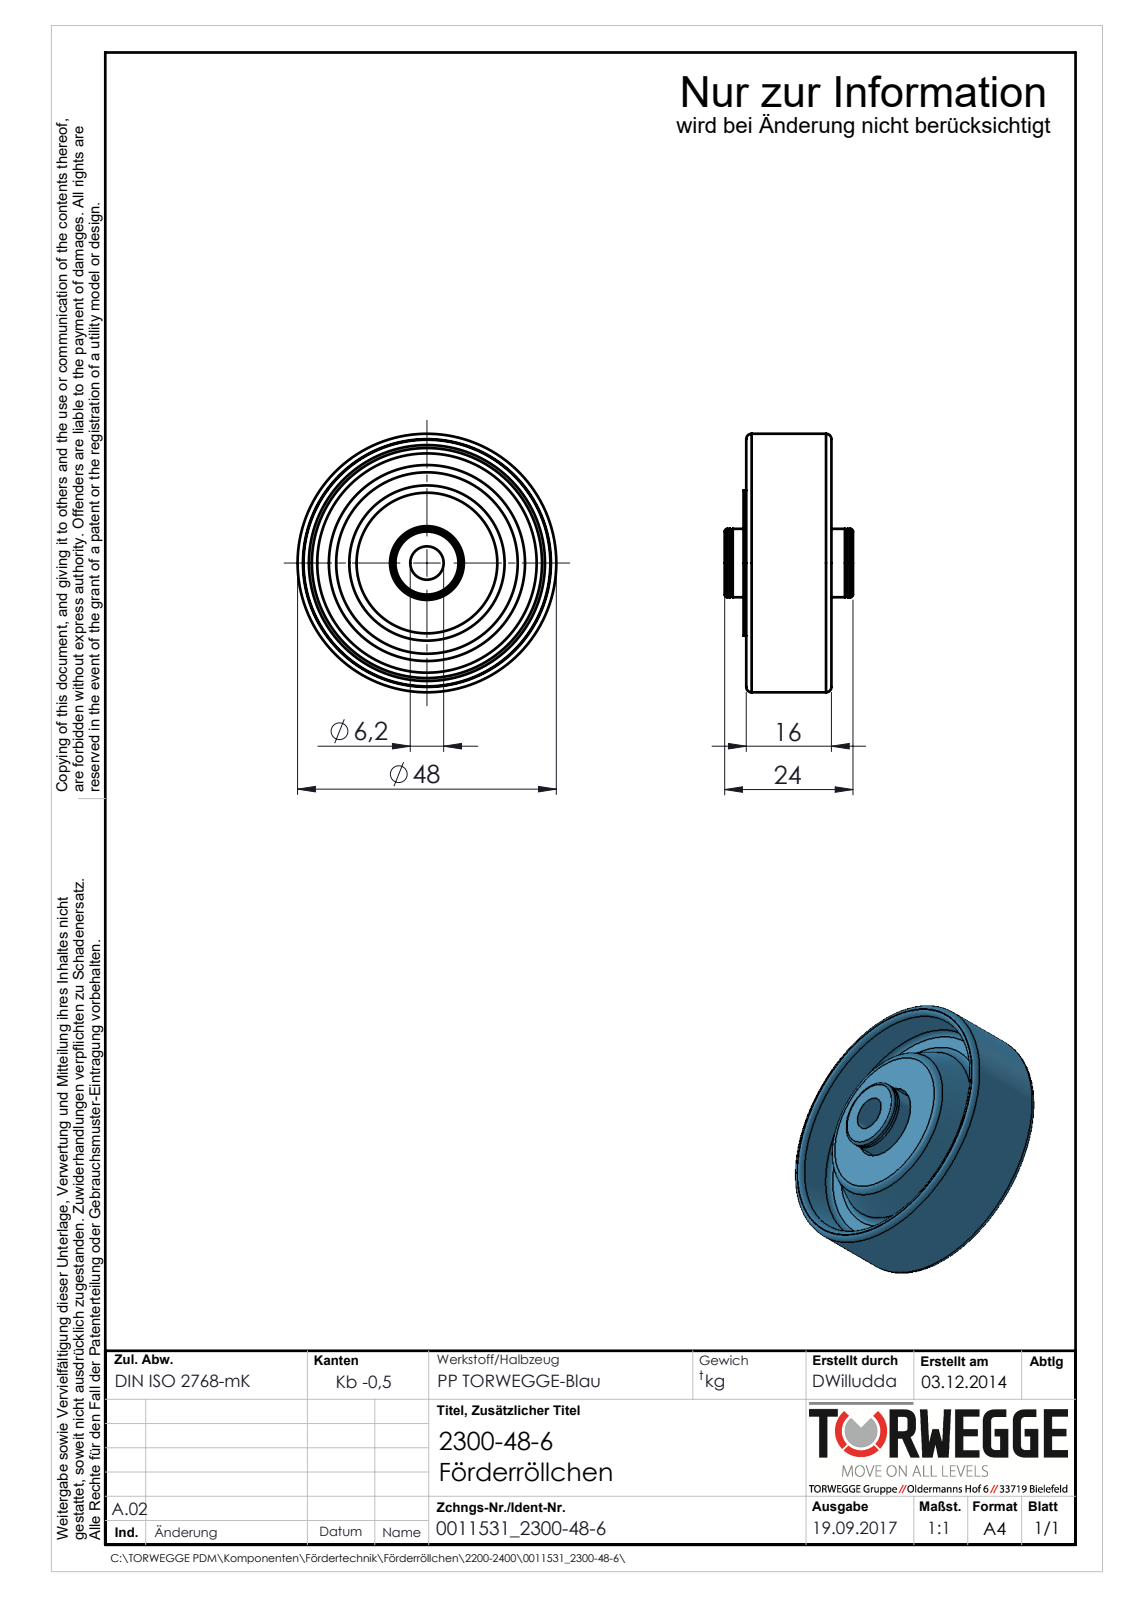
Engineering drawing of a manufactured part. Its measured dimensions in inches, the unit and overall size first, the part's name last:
Units: inches
Overall size (bounding box): 1.89 × 1.89 × 0.937
Round holes (diameter × count): ⌀0.244 ×1, ⌀0.539 ×1
Round bosses / shafts (diameter × count): ⌀1.89 ×1, ⌀1.063 ×1, ⌀0.5 ×1
Main face-to-face distances: 0.642, 0.356, 0.266, 0.285, 0.091, 0.376, 0.423, 0.514, 0.157, 0.138
Volume: 1.187 in³ · Surface area: 14.67 in²
Bodies: 1 solid, 69 faces (11 planar, 18 cylindrical, 40 other)
Part name (STEP PRODUCT): 0011531_2300-48-6
STEP written by: SolidWorks 2016 (AUTOMOTIVE_DESIGN)
